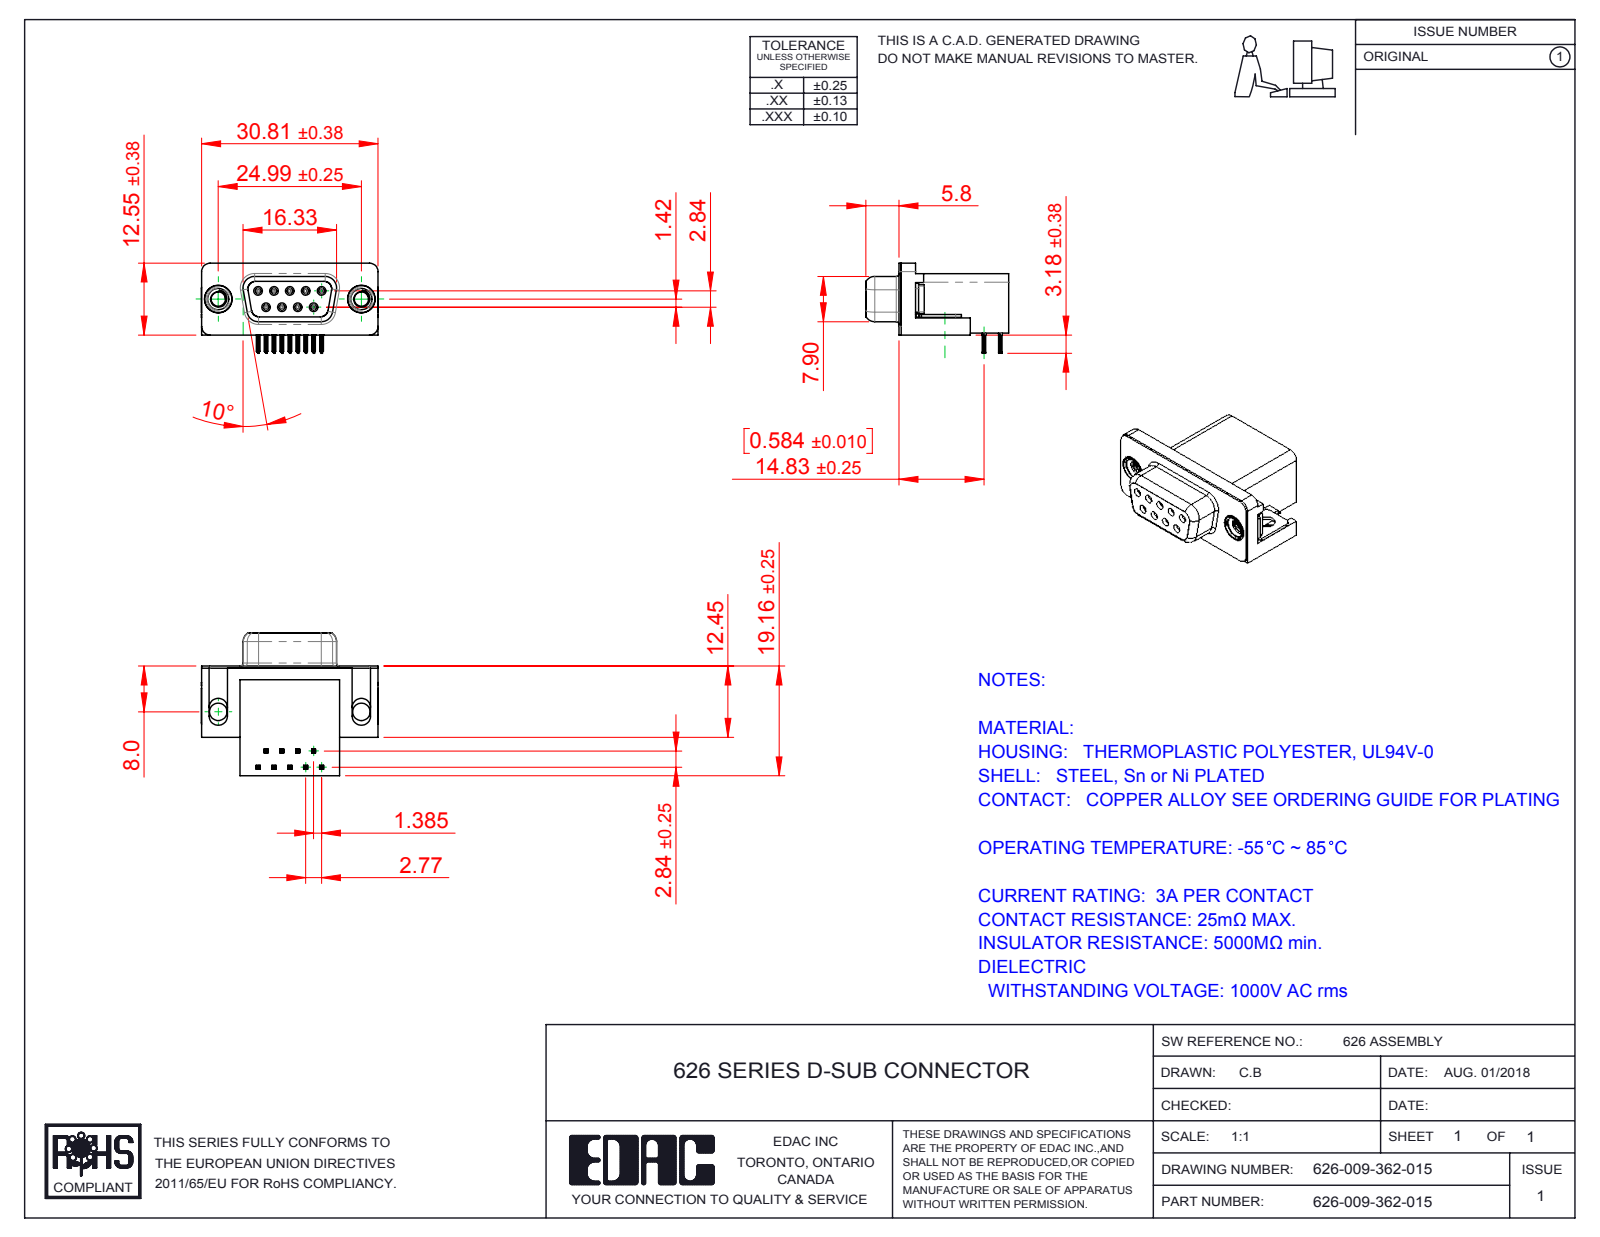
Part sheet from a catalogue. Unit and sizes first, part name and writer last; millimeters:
Units: millimetres
Overall size (bounding box): 30.89 × 24.96 × 15.73
Round holes (diameter × count): ⌀0.8 ×9, ⌀0.9 ×9, ⌀2.5 ×2, ⌀3.05 ×2, ⌀4 ×2, ⌀4.8 ×2, ⌀5 ×2
Round bosses / shafts (diameter × count): ⌀1.2 ×9, ⌀4.9 ×2, ⌀4.75 ×2, ⌀3.9 ×2
Partial cylindrical surfaces — rounded edges, fillets, slot ends (radius × count): R0.1 ×72, R0.15 ×36, R0.35 ×18, R1 ×18, R0.34 ×9, R0.25 ×8, R1.35 ×8, R1.6 ×8
Main face-to-face distances: 0.4, 10.34, 0.35, 18.76, 19.16, 2.9, 2.5, 6.2, 16.26, 0.5
Hole centre spacings: 3.16, 2.77, 5.54, 5.03, 5.04, 8.31, 7.48, 7.49
Volume: 4 961 mm³ · Surface area: 5 781 mm²
Bodies: 15 solids, 1572 faces (684 planar, 420 cylindrical, 468 other)
Part name (STEP PRODUCT): 626 M3 Threaded Rivet; 626-009-362-015; 626 Thru Hole Board Mount; 626 Contact Top (+3 more)
STEP written by: SolidWorks 2016 (CONFIG_CONTROL_DESIGN)
